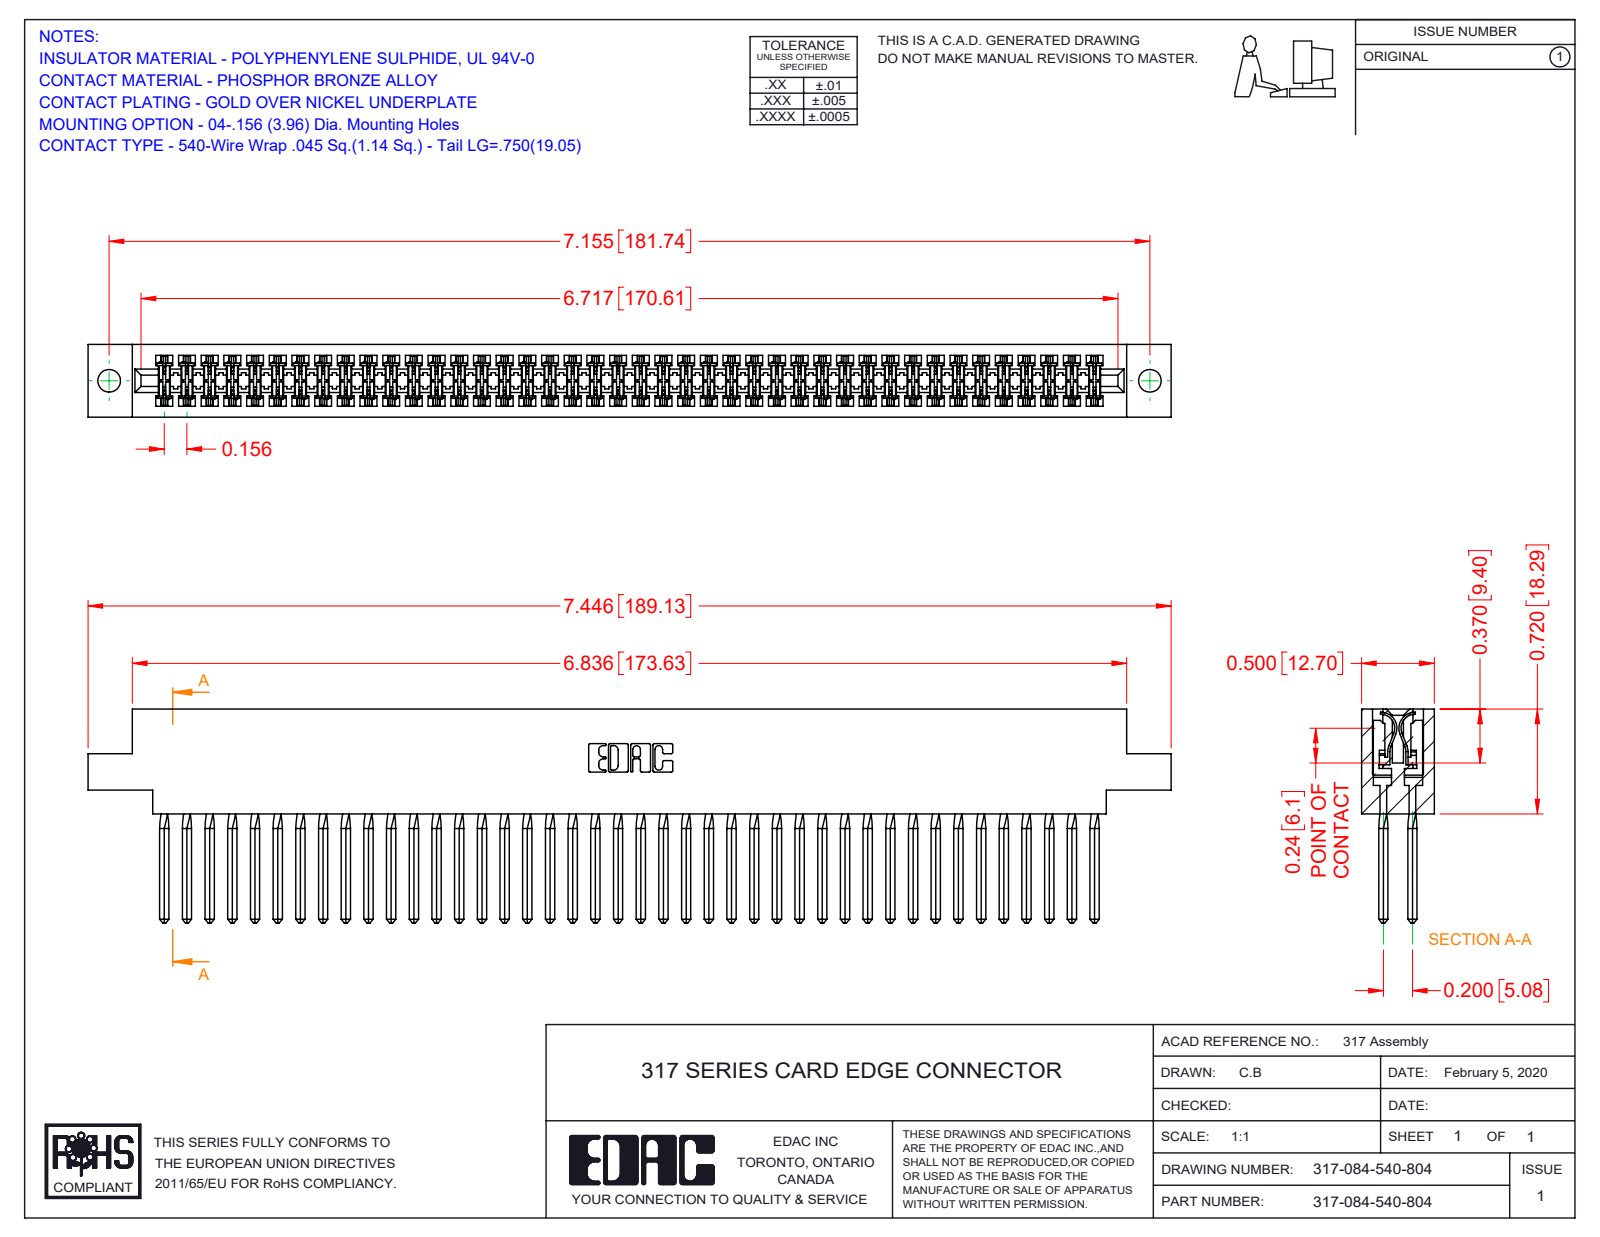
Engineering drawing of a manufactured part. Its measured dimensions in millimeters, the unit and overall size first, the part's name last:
Units: millimetres
Overall size (bounding box): 189.1 × 37.3 × 12.7
Round holes (diameter × count): ⌀4 ×2
Partial cylindrical surfaces — rounded edges, fillets, slot ends (radius × count): R0.4 ×168, R0.3 ×22, R0.2 ×6, R0.8 ×6, R0.7 ×3, R2.4 ×2, R2.5 ×2, R2.8 ×2
Main face-to-face distances: 12.7, 1.9, 10.8, 8.9, 5, 2.4, 5.1, 2.9, 3.3, 1.2
Hole centre spacings: 181.7
Volume: 31 660 mm³ · Surface area: 47 020 mm²
Bodies: 85 solids, 7578 faces (6190 planar, 1052 cylindrical, 336 other)
Part name (STEP PRODUCT): 317-084-540-804; 317 Part_.156 Dia - TH; 317-290-001_540
STEP written by: SolidWorks 2016 (CONFIG_CONTROL_DESIGN)
